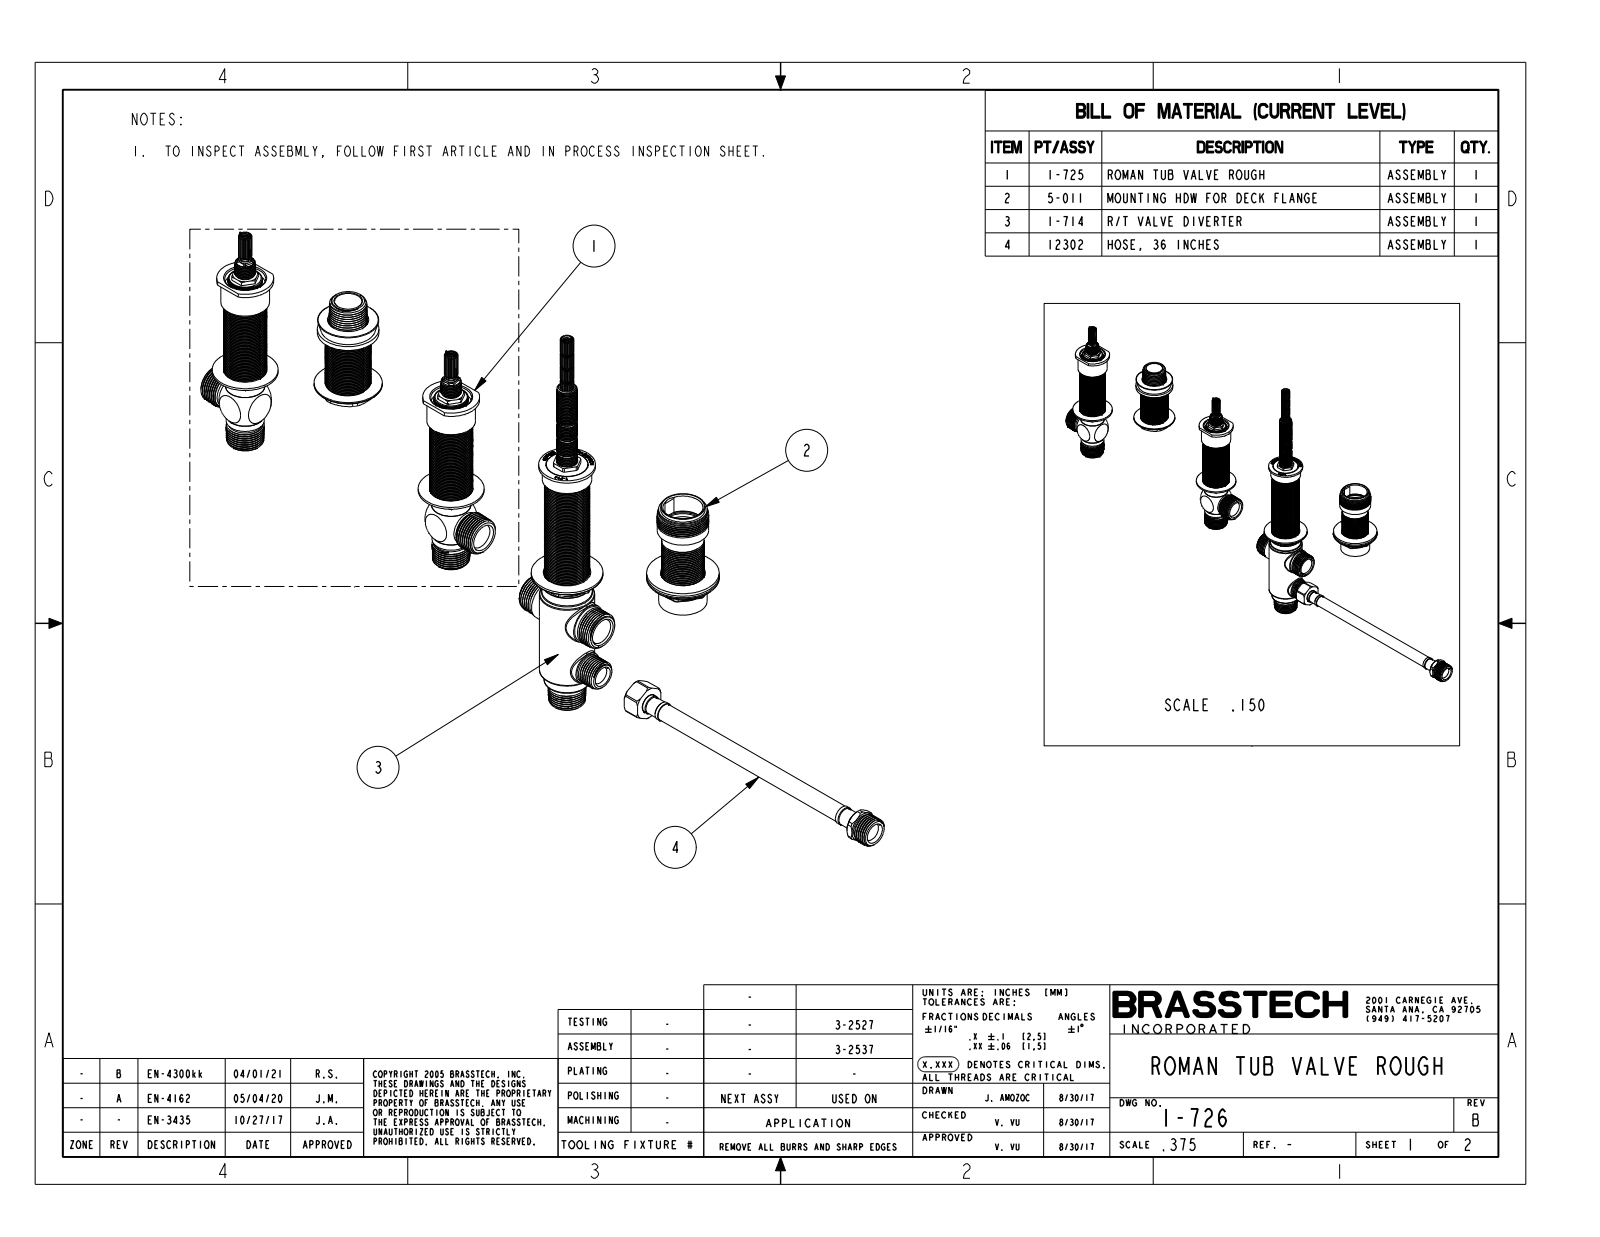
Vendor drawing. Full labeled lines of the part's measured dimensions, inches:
Part name (STEP PRODUCT): 1-726
STEP written by: CREO PARAMETRIC BY PTC INC, 2018400 (AUTOMOTIVE_DESIGN)
Units: inches
Bodies: 7 solids, 3829 faces (1040 planar, 1436 cylindrical, 1353 other)
Overall size (bounding box): 24.179 × 12.184 × 2
Volume: 33.09 in³ · Surface area: 281.6 in²
Round holes (diameter × count): ⌀1.12 ×3, ⌀0.196 ×2, ⌀0.201 ×2, ⌀0.138 ×1, ⌀0.202 ×1, ⌀0.274 ×1, ⌀0.393 ×1, ⌀0.394 ×1, ⌀0.48 ×1, ⌀0.52 ×1, ⌀0.535 ×1, ⌀0.595 ×1
Round bosses / shafts (diameter × count): ⌀1.811 ×2, ⌀1.335 ×2, ⌀1.187 ×2, ⌀1.11 ×2, ⌀1.075 ×2, ⌀1.047 ×2, ⌀0.945 ×2, ⌀0.929 ×2
Partial cylindrical surfaces — rounded edges, fillets, slot ends (radius × count): R0.04 ×14, R0.08 ×8, R0.039 ×6, R0.15 ×6, R0.164 ×3, R0.06 ×2, R0.26 ×2, R0.3 ×2
Main face-to-face distances: 2.126, 3.089, 0.061, 0.571, 1.526, 1.563, 1.637, 1.587, 3.15, 1.72
Hole centre spacings: 4.5, 2.362, 8, 9, 12.5, 17
